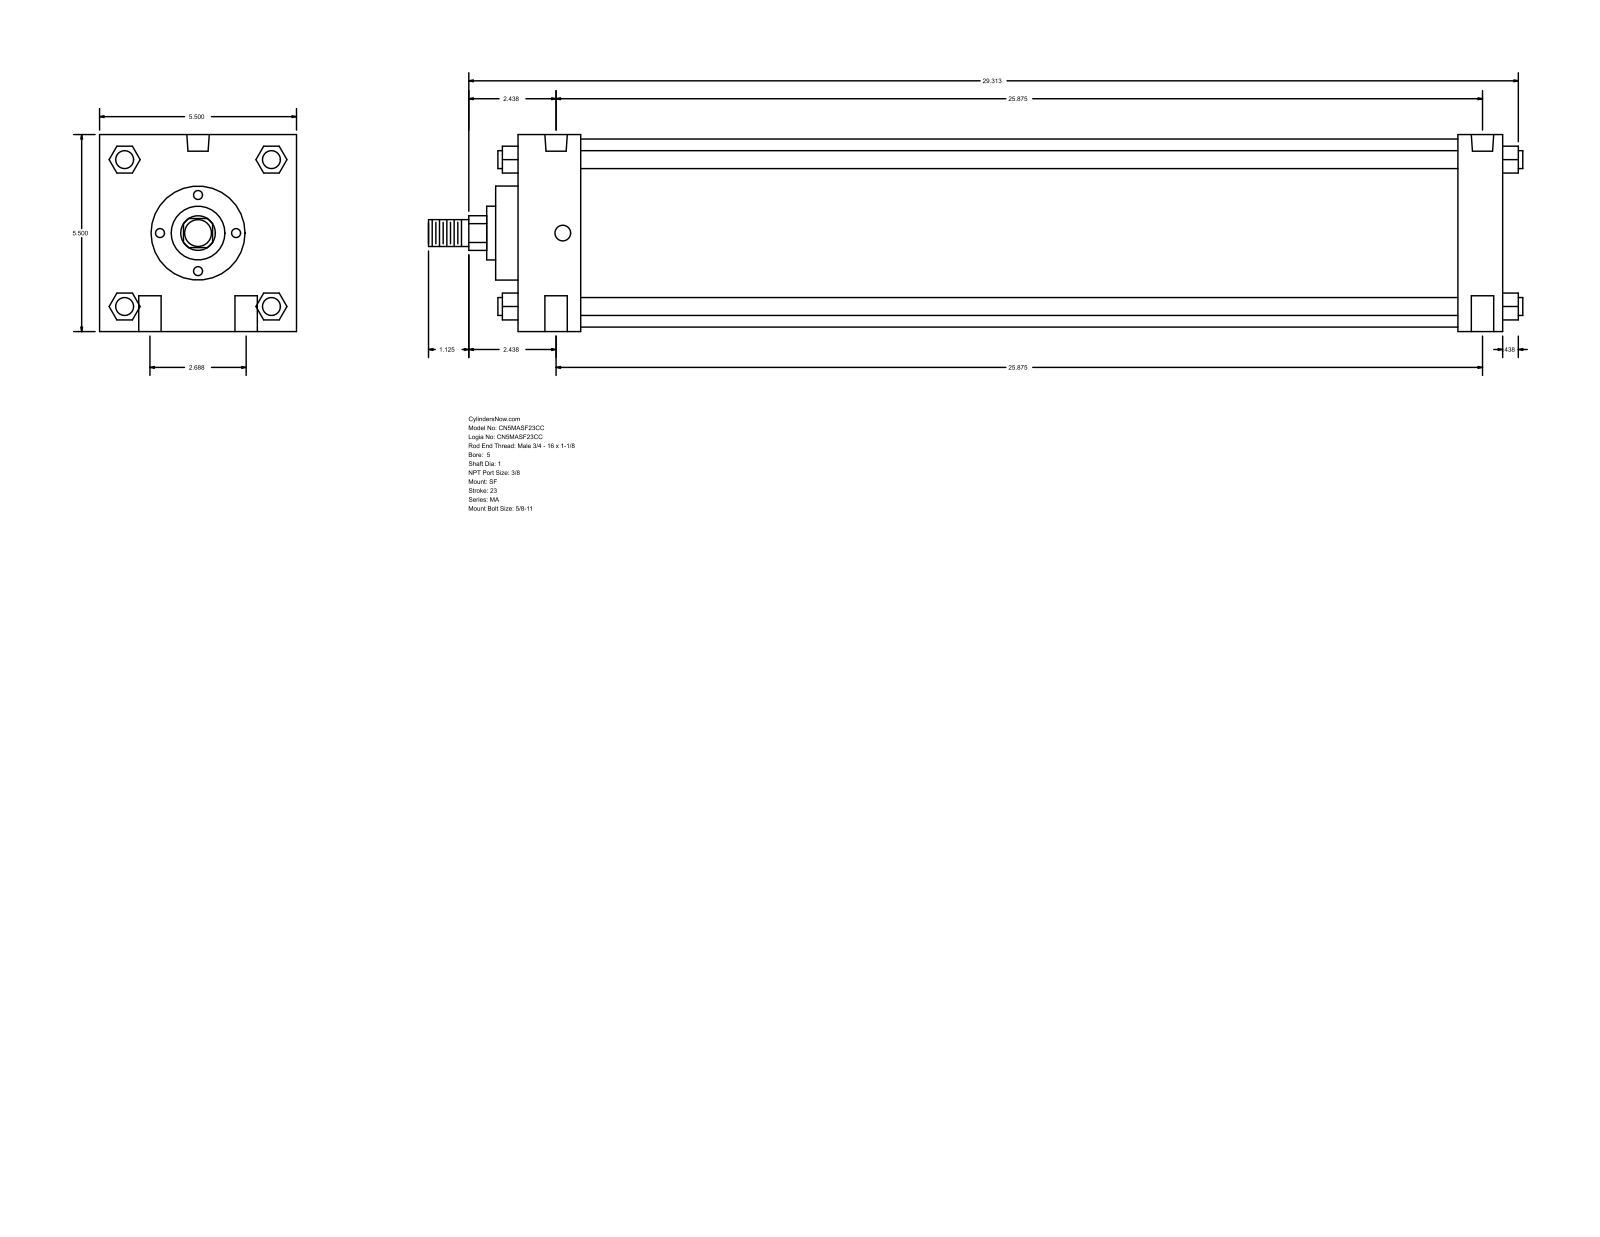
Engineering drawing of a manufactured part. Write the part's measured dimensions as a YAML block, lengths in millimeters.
part_name: "MA_SF__0500_1"
step_written_by: "GSSL Pune (CONFIG_CONTROL_DESIGN)"
units: millimeters
bodies: {solids: 0, faces: 126, planar: 95, cylindrical: 31, other: 0}
overall_size: [776.29, 139.7, 139.7]
round_holes:
  - {diameter: 15.88, count: 4}
  - {diameter: 11.11, count: 2}
  - {diameter: 15.93, count: 2}
round_bosses_or_shafts:
  - {diameter: 12.7, count: 4}
  - {diameter: 133.35, count: 1}
  - {diameter: 66.67, count: 1}
  - {diameter: 38.1, count: 1}
  - {diameter: 25.4, count: 1}
  - {diameter: 19.05, count: 1}
partial_cylinders:
  - {radius: 12.29, count: 1}
face_to_face_distances: [139.7, 698.5, 44.46, 666.75, 622.29, 654.04, 31.75, 15.87, 60.33, 682.62]
hole_center_spacings: [34.13, 658.12, 657.23, 68.26, 660.77, 647.71]
